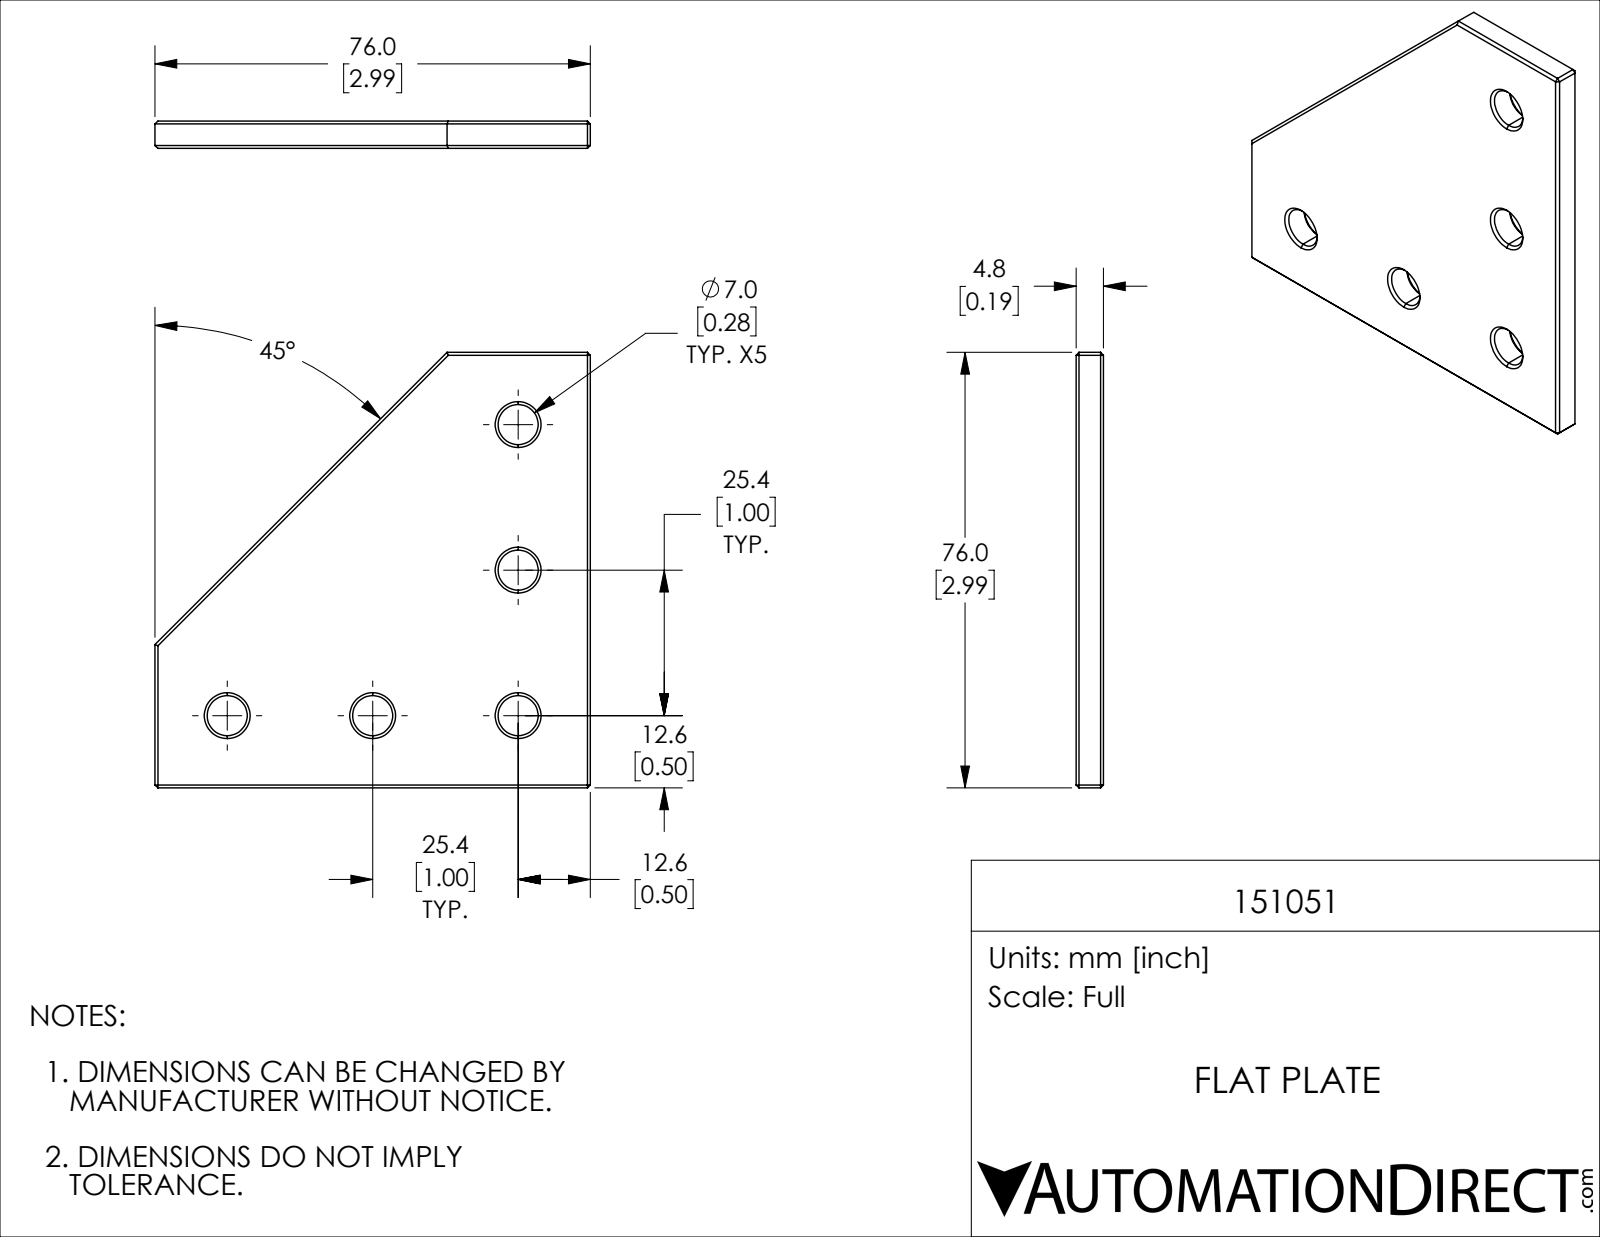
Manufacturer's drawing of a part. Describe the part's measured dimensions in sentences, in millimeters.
The part is named "151051". Its 3-D file was written by "SolidWorks 2021 (CONFIG_CONTROL_DESIGN)". It is 1 solid with 56 faces: 26 planar, 10 cylindrical and 20 other. Overall it measures 76 by 76 by 4.76 millimeters. Its volume is 20 300 cubic millimeters and its surface area 10 169 square millimeters. Round holes: 5 of diameter 7. The main face-to-face distances are 4.76, 76, 56.39, 106.76, 71.06, 89.29. The hole center spacings are 25.4, 50.8, 56.8, 35.92, 71.84.
